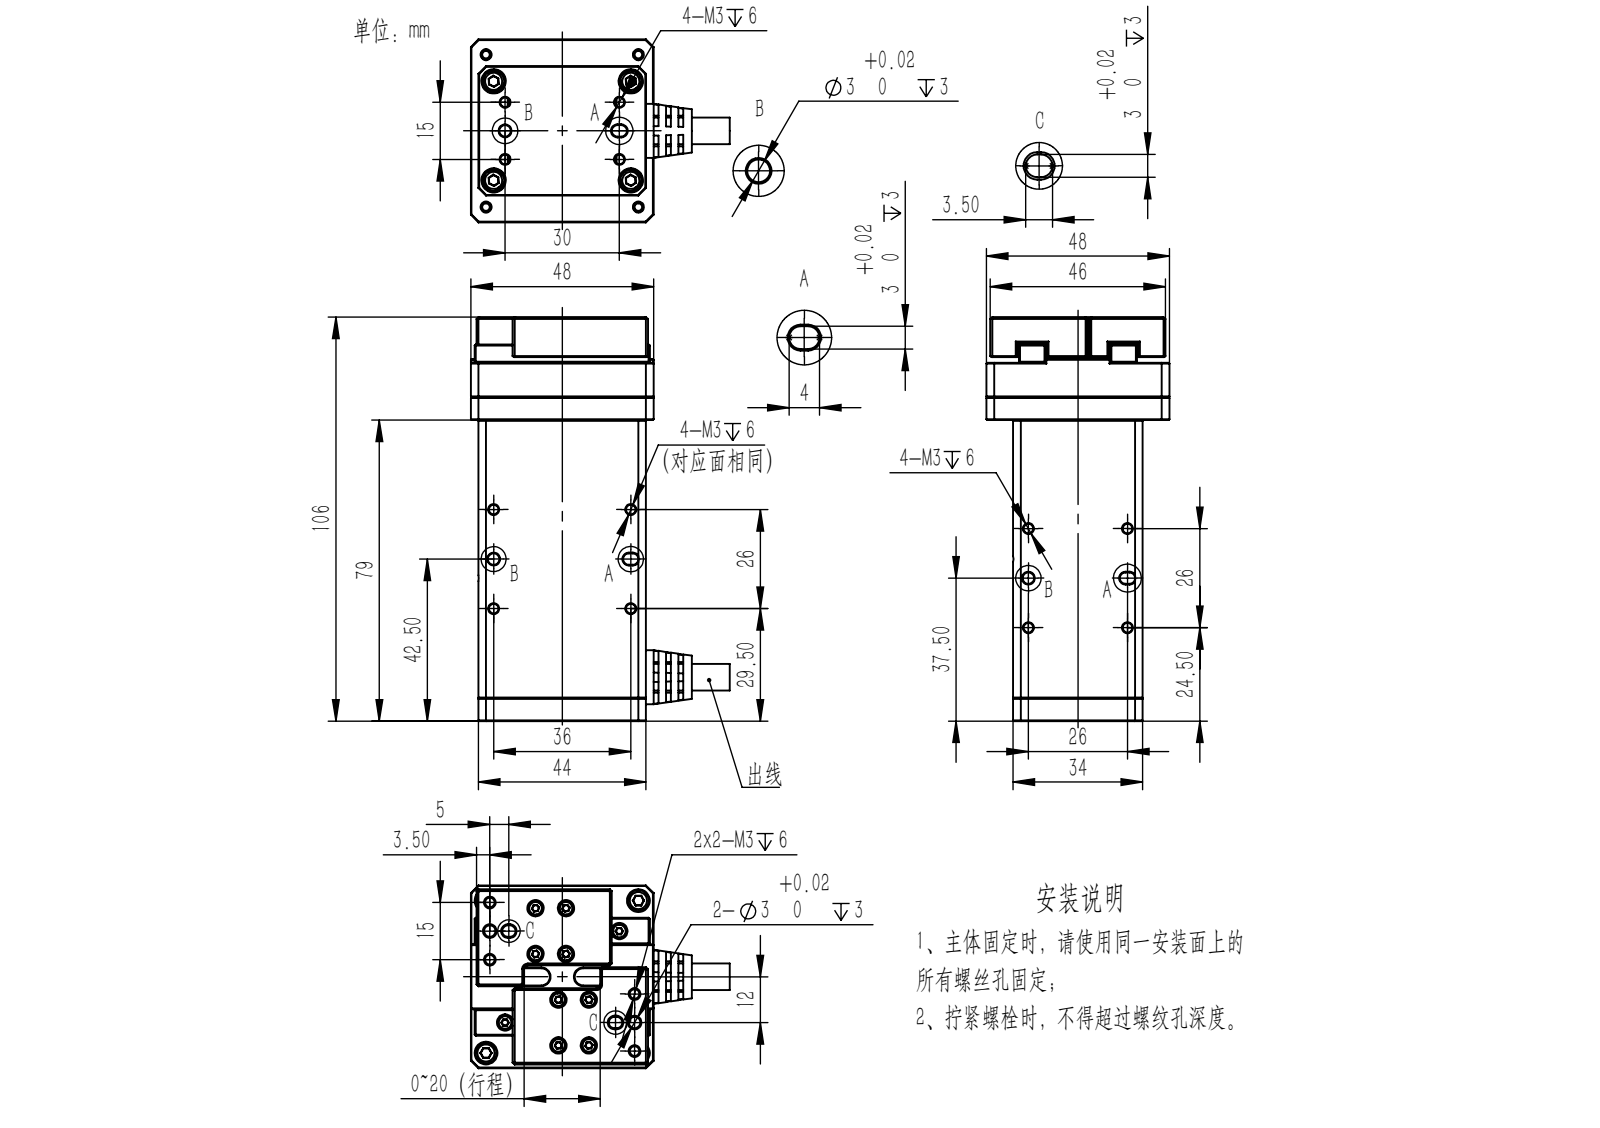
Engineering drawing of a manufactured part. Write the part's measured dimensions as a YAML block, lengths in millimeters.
part_name: "SR.step"
step_written_by: "SolidWorks 2019 (CONFIG_CONTROL_DESIGN)"
units: millimeters
bodies: {solids: 33, faces: 1735, planar: 949, cylindrical: 410, other: 376}
overall_size: [106, 68, 48]
volume: 70333
surface_area: 57733
round_holes:
  - {diameter: 2.5, count: 24}
  - {diameter: 1.6, count: 14}
  - {diameter: 2.4, count: 14}
  - {diameter: 4.3, count: 14}
  - {diameter: 3, count: 10}
  - {diameter: 3.4, count: 8}
  - {diameter: 6, count: 8}
  - {diameter: 2.7, count: 4}
  - {diameter: 5, count: 4}
  - {diameter: 22.2, count: 1}
  - {diameter: 42, count: 1}
round_bosses_or_shafts:
  - {diameter: 3.7, count: 14}
  - {diameter: 2, count: 14}
  - {diameter: 5.5, count: 8}
  - {diameter: 3, count: 8}
  - {diameter: 14.2, count: 1}
  - {diameter: 7, count: 1}
partial_cylinders:
  - {radius: 1, count: 14}
  - {radius: 1.5, count: 14}
  - {radius: 2, count: 12}
  - {radius: 3, count: 8}
  - {radius: 2.25, count: 4}
  - {radius: 4.05, count: 1}
  - {radius: 4.15, count: 1}
  - {radius: 4.5, count: 1}
face_to_face_distances: [1.5, 32.5, 6, 4, 12, 34, 5, 2, 7, 44]
hole_center_spacings: [26, 32.63, 15, 12, 12.02, 13, 18.03, 19.21]
